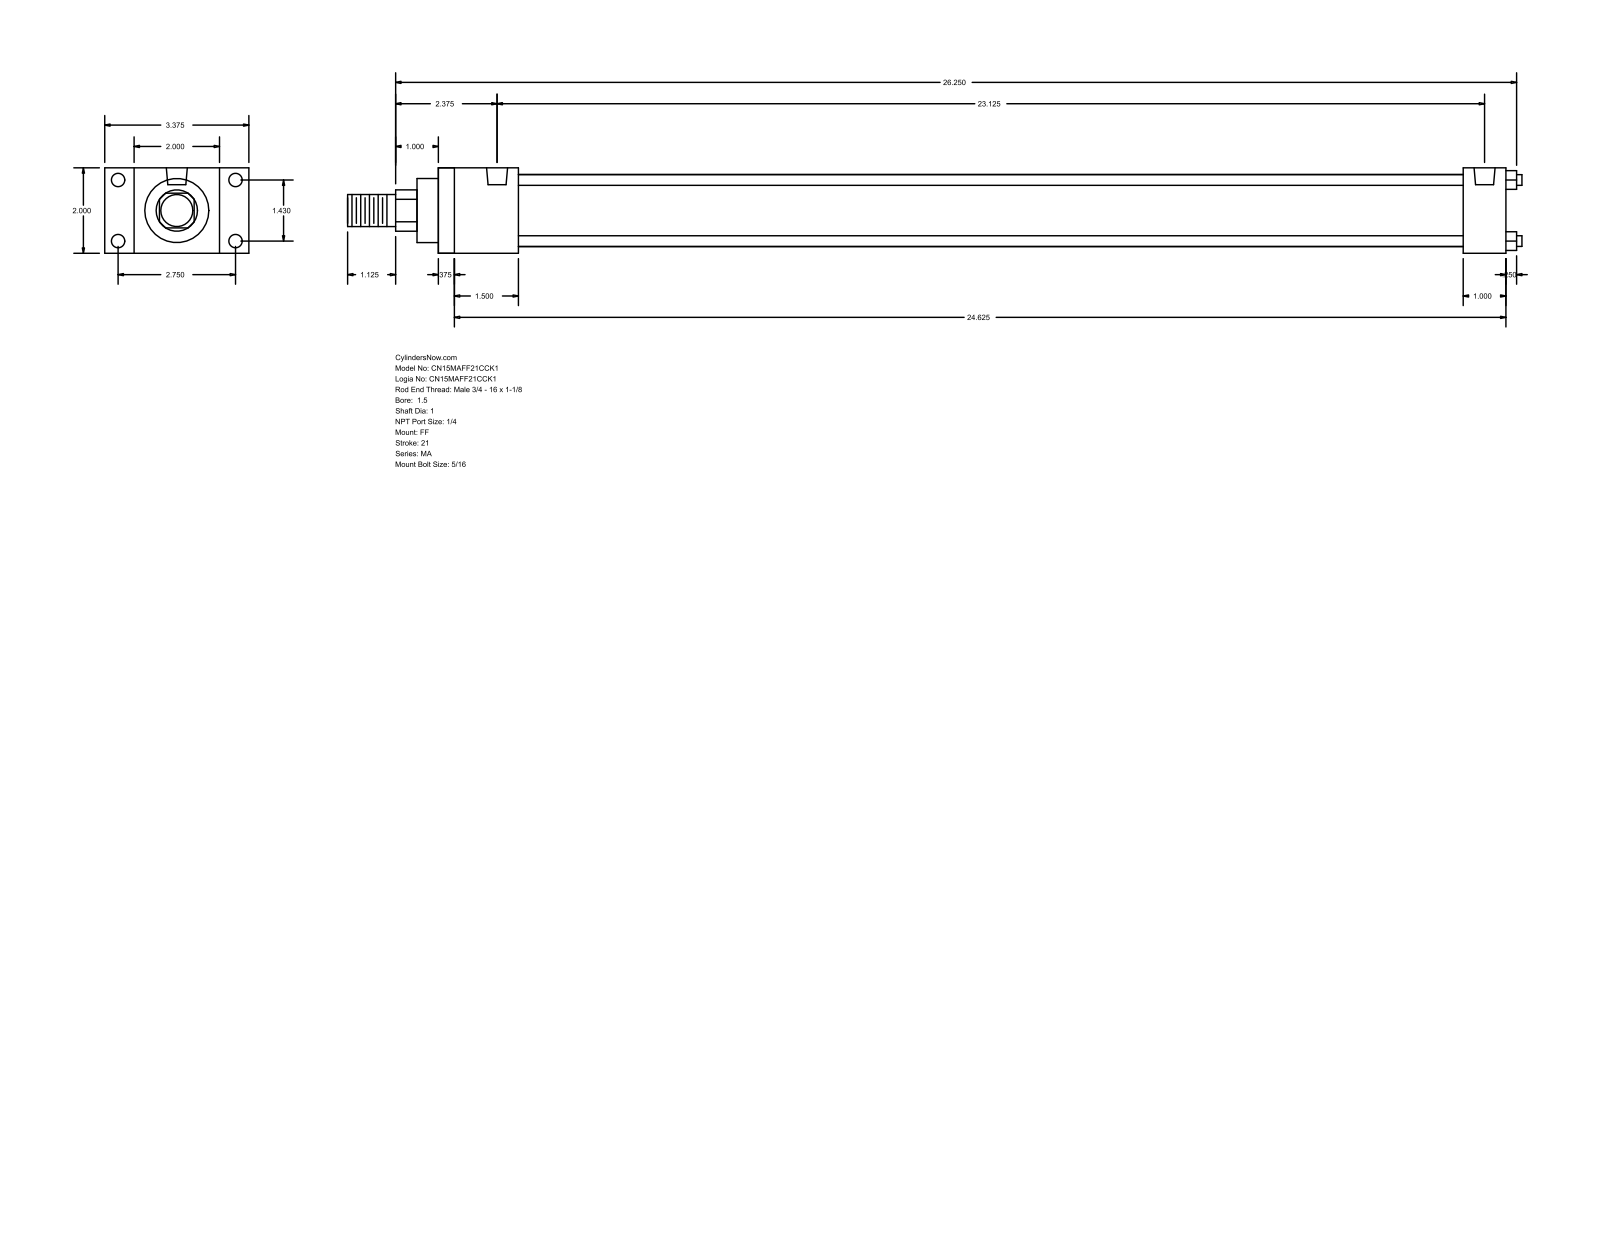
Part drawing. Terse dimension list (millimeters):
name: MA_FF__0150_1
written by: GSSL Pune (CONFIG_CONTROL_DESIGN)
unit: mm
bodies: 0 solids, 92 faces (64 planar, 28 cylindrical, 0 other)
size: 698.5 × 85.72 × 50.8
holes: 8× ⌀7.94, 2× ⌀12.49
bosses: 4× ⌀6.35, 1× ⌀42.93, 1× ⌀38.1, 1× ⌀25.4, 1× ⌀19.05
rounds: 1× R12.29
face distances: 50.8, 635, 9.52, 625.48, 25.4, 47.63, 609.6, 38.11, 600.08, 561.97
hole spacings: 36.32, 69.84, 78.72, 587.37
